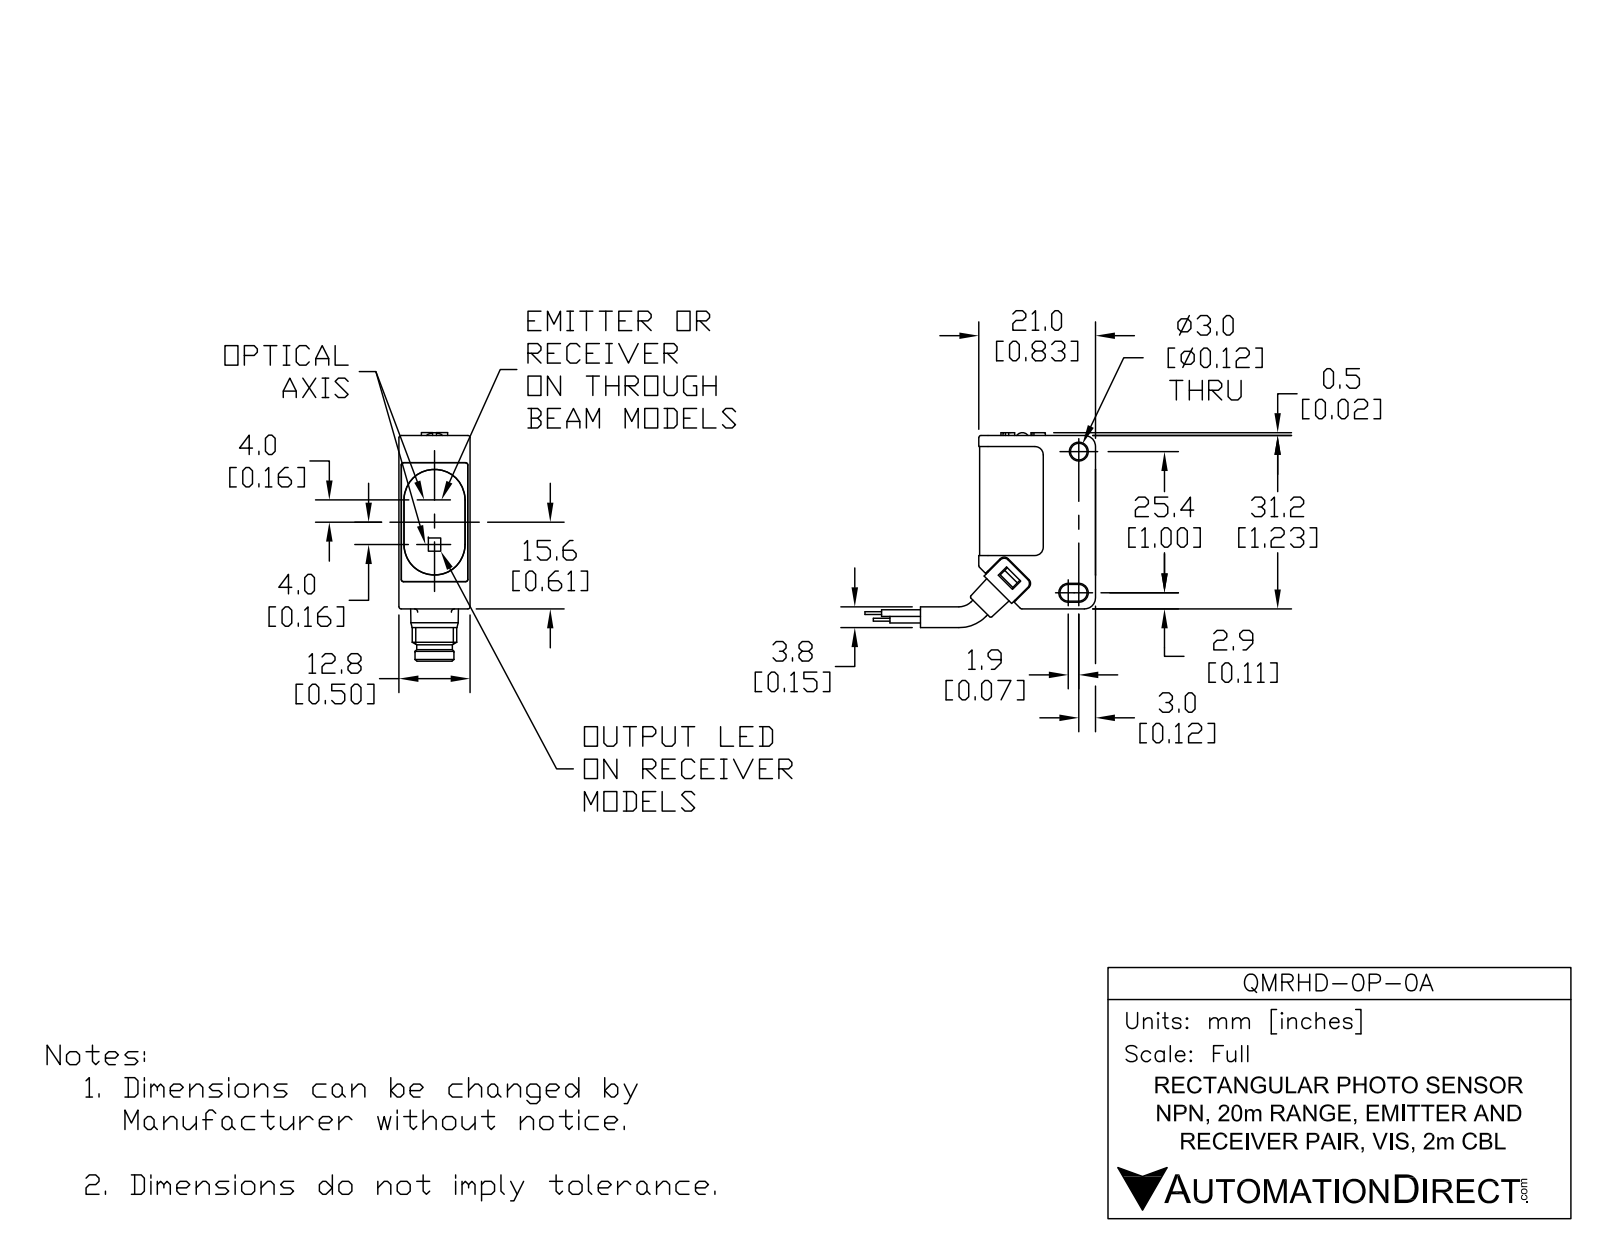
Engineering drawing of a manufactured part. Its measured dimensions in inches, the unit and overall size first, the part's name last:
Units: inches
Overall size (bounding box): 3.193 × 1.032 × 0.512
Round holes (diameter × count): ⌀0.118 ×3, ⌀0.148 ×1, ⌀0.224 ×1, ⌀0.283 ×1
Round bosses / shafts (diameter × count): ⌀0.138 ×2
Partial cylindrical surfaces — rounded edges, fillets, slot ends (radius × count): R0.016 ×13, R0.02 ×10, R0.039 ×8, R0.059 ×6, R0.024 ×4, R0.006 ×2, R0.035 ×2, R0.044 ×2
Main face-to-face distances: 0.02, 0.498, 0.059, 0.016, 0.504, 0.138, 0.488, 0.079, 0.482, 0.492
Hole centre spacings: 0.205
Volume: 0.47 in³ · Surface area: 8.375 in²
Bodies: 9 solids, 258 faces (134 planar, 100 cylindrical, 24 other)
Part name (STEP PRODUCT): QMRHD-0P-0A
STEP written by: SolidWorks 2017 (AUTOMOTIVE_DESIGN)
